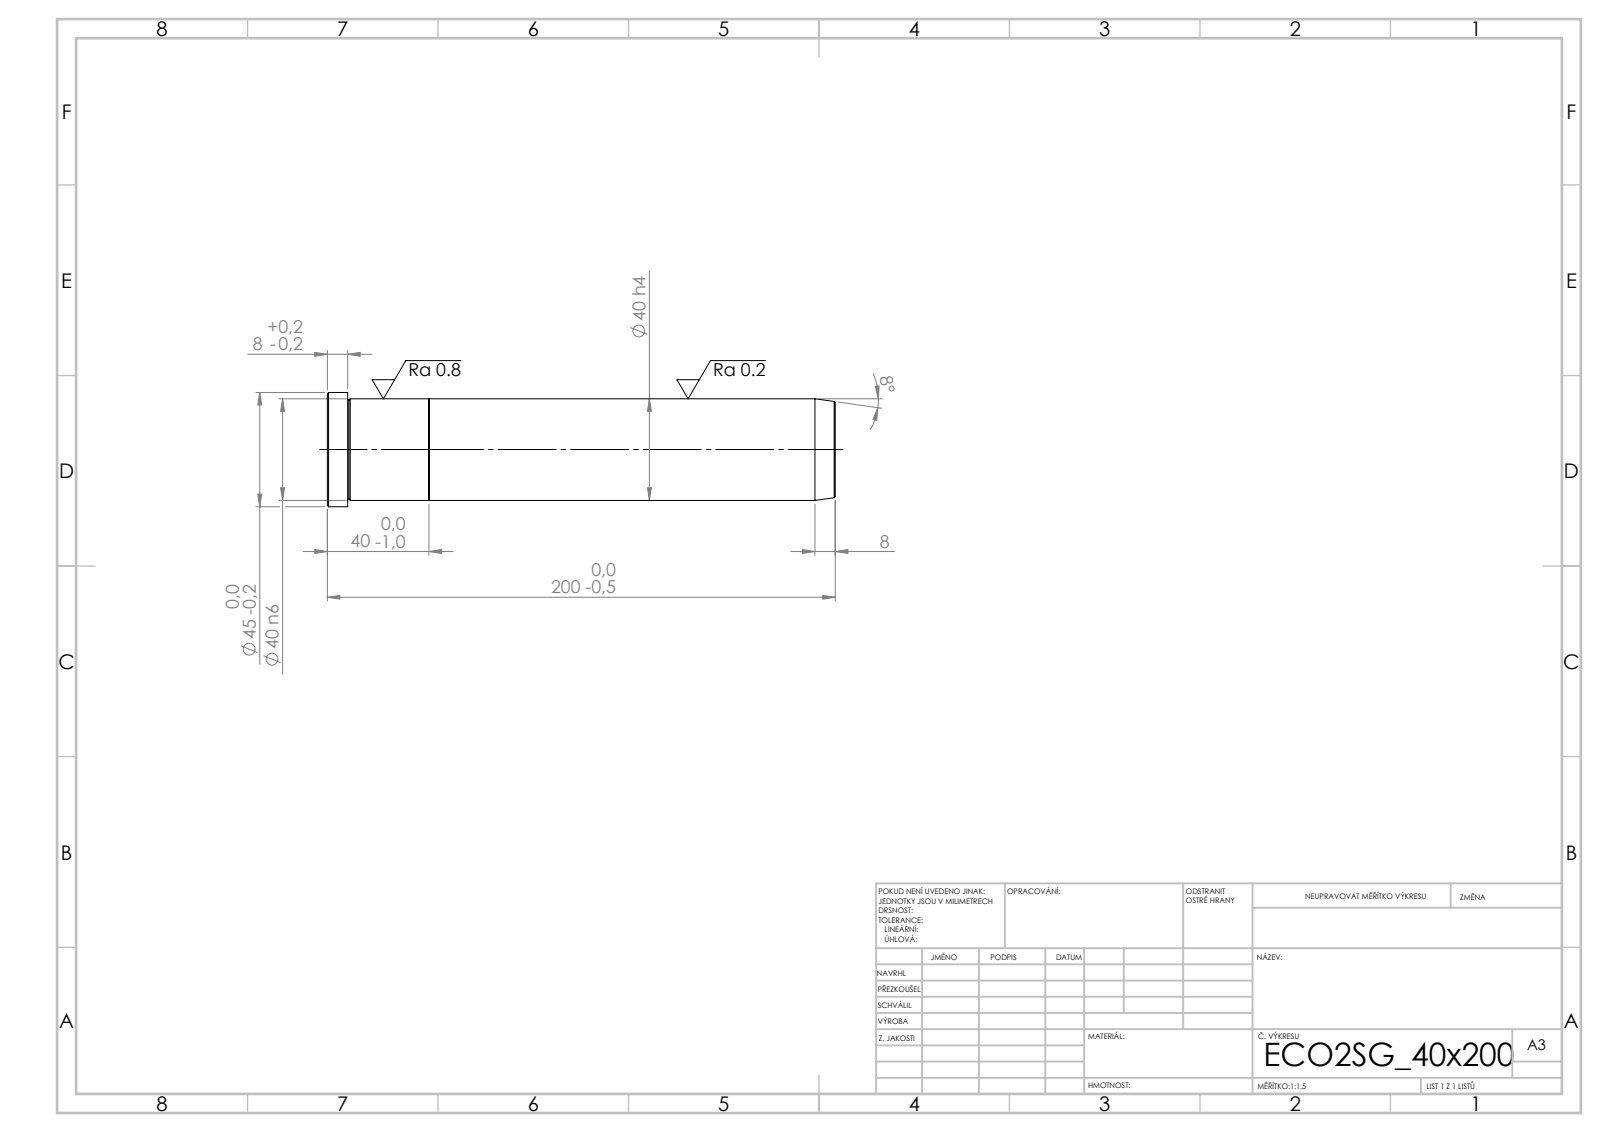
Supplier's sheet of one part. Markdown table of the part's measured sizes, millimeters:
| quantity | value |
| --- | --- |
| STEP written by | SolidWorks 2019 (CONFIG_CONTROL_DESIGN) |
| units | millimeters |
| bodies | 2 solids, 21 faces (5 planar, 6 cylindrical, 10 other) |
| overall size | 200 × 45 × 45 |
| volume | 253 372 mm³ |
| surface area | 30 805 mm² |
| round bosses / shafts (diameter × count) | 45 × 1, 40 × 1 |
| main face-to-face distances | 40, 160, 200, 192, 32, 8 |
